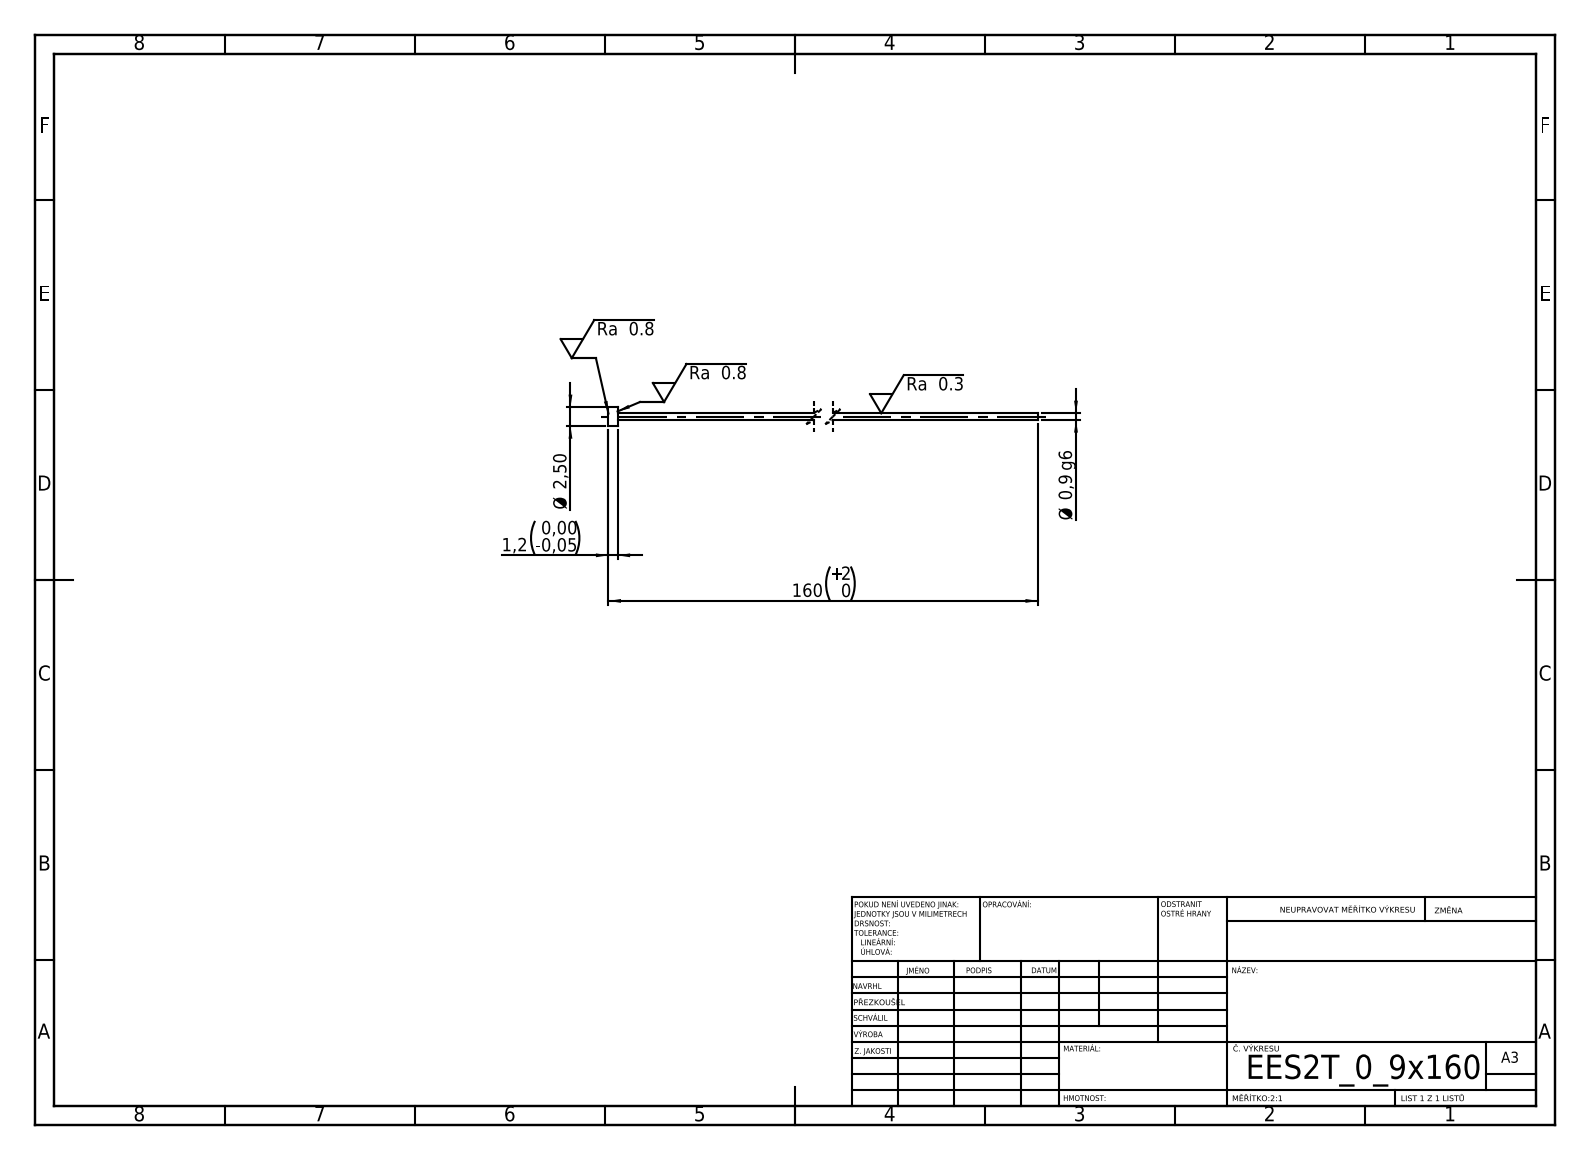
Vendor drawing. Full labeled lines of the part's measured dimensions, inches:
STEP written by: SolidWorks 2019 (CONFIG_CONTROL_DESIGN)
Units: inches
Bodies: 1 solid, 7 faces (3 planar, 4 cylindrical, 0 other)
Overall size (bounding box): 6.299 × 0.098 × 0.098
Volume: 0.007 in³ · Surface area: 0.725 in²
Round bosses / shafts (diameter × count): ⌀0.098 ×1, ⌀0.035 ×1
Main face-to-face distances: 0.047, 6.299, 6.252
